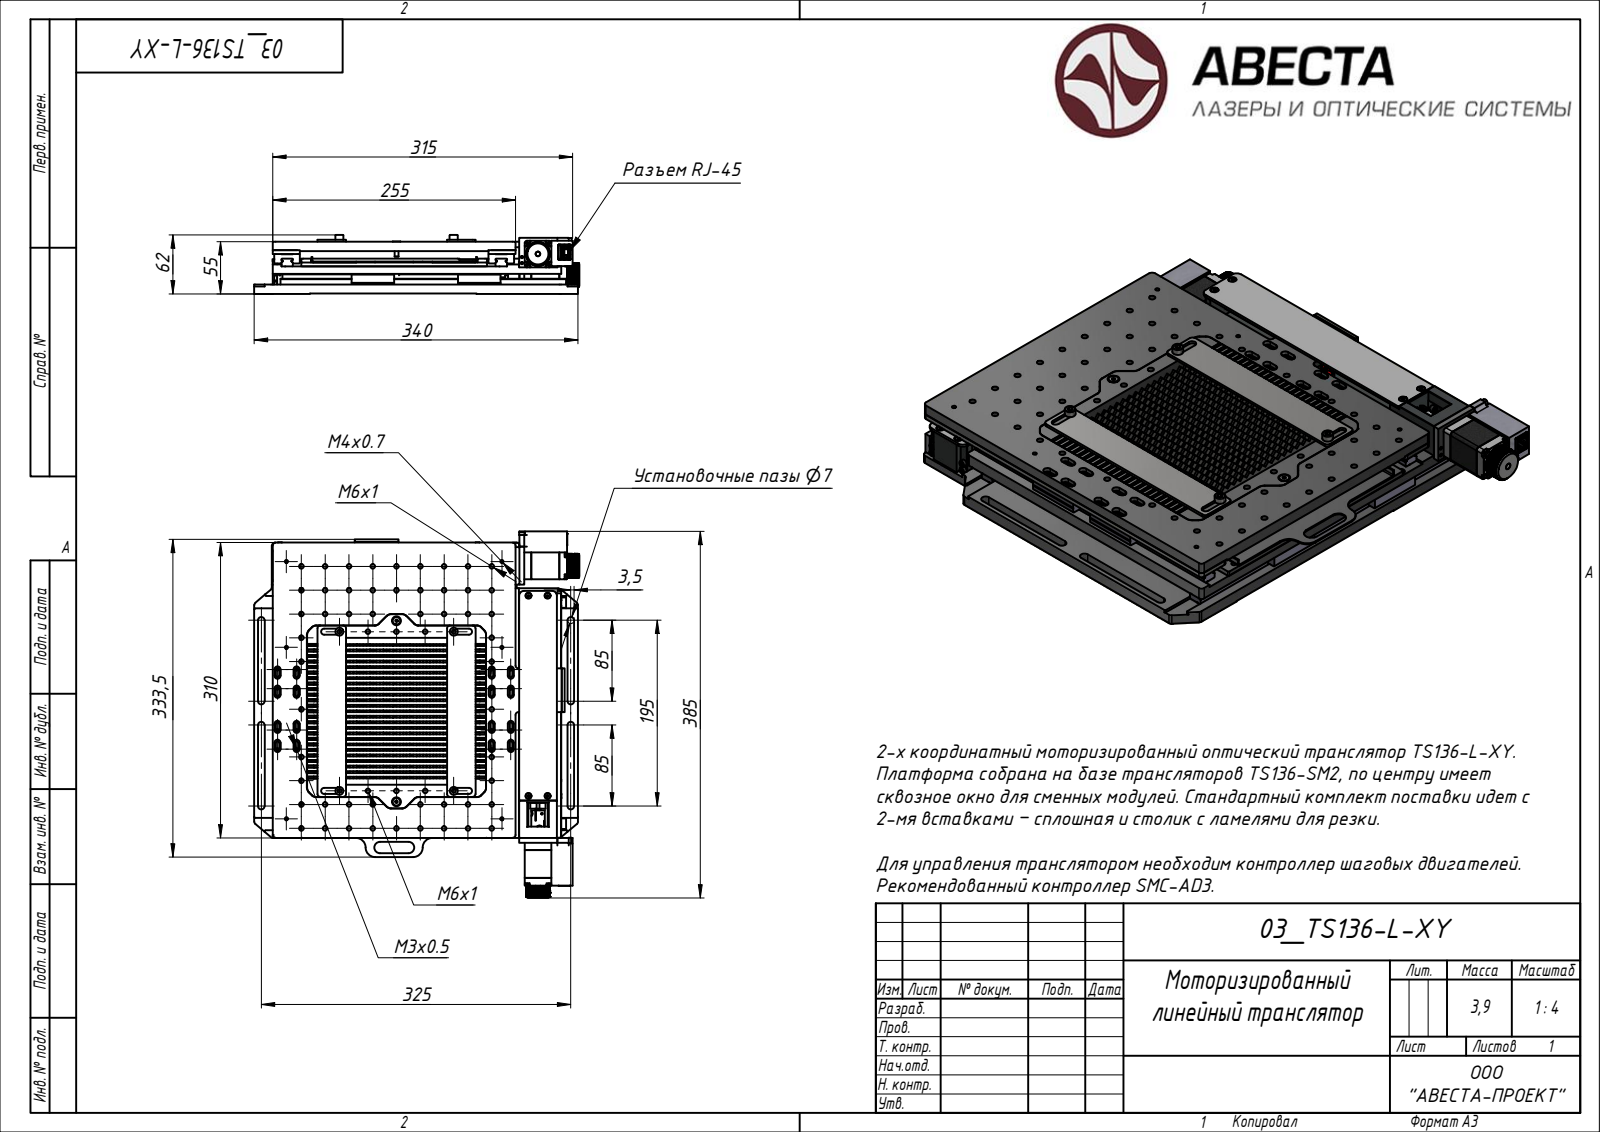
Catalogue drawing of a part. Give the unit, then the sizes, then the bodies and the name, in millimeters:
Units: millimetres
Overall size (bounding box): 384.9 × 341.5 × 62
Round holes (diameter × count): ⌀3.5 ×47, ⌀6 ×44, ⌀2.46 ×38, ⌀2.46 ×37, ⌀4.92 ×35, ⌀6.5 ×28, ⌀4.92 ×26, ⌀3.4 ×20, ⌀3.24 ×18, ⌀4.1 ×18, ⌀2.5 ×12, ⌀1.05 ×10
Round bosses / shafts (diameter × count): ⌀4.5 ×20, ⌀5.5 ×11, ⌀5 ×10, ⌀5.3 ×8, ⌀2.5 ×8, ⌀8.5 ×4, ⌀8 ×4, ⌀6 ×4
Partial cylindrical surfaces — rounded edges, fillets, slot ends (radius × count): R0.5 ×80, R3 ×65, R0.25 ×48, R6 ×48, R1.7 ×40, R2 ×30, R3.25 ×28, R1 ×22
Main face-to-face distances: 21, 24, 34, 11, 12, 13, 10, 45, 22, 8
Hole centre spacings: 18, 20, 1, 16.26, 23, 297, 2, 288.3
Volume: 2 350 000 mm³ · Surface area: 840 809 mm²
Bodies: 1 solid, 7437 faces (4838 planar, 2175 cylindrical, 424 other)
STEP written by: Rhino 7.34 (AUTOMOTIVE_DESIGN)
